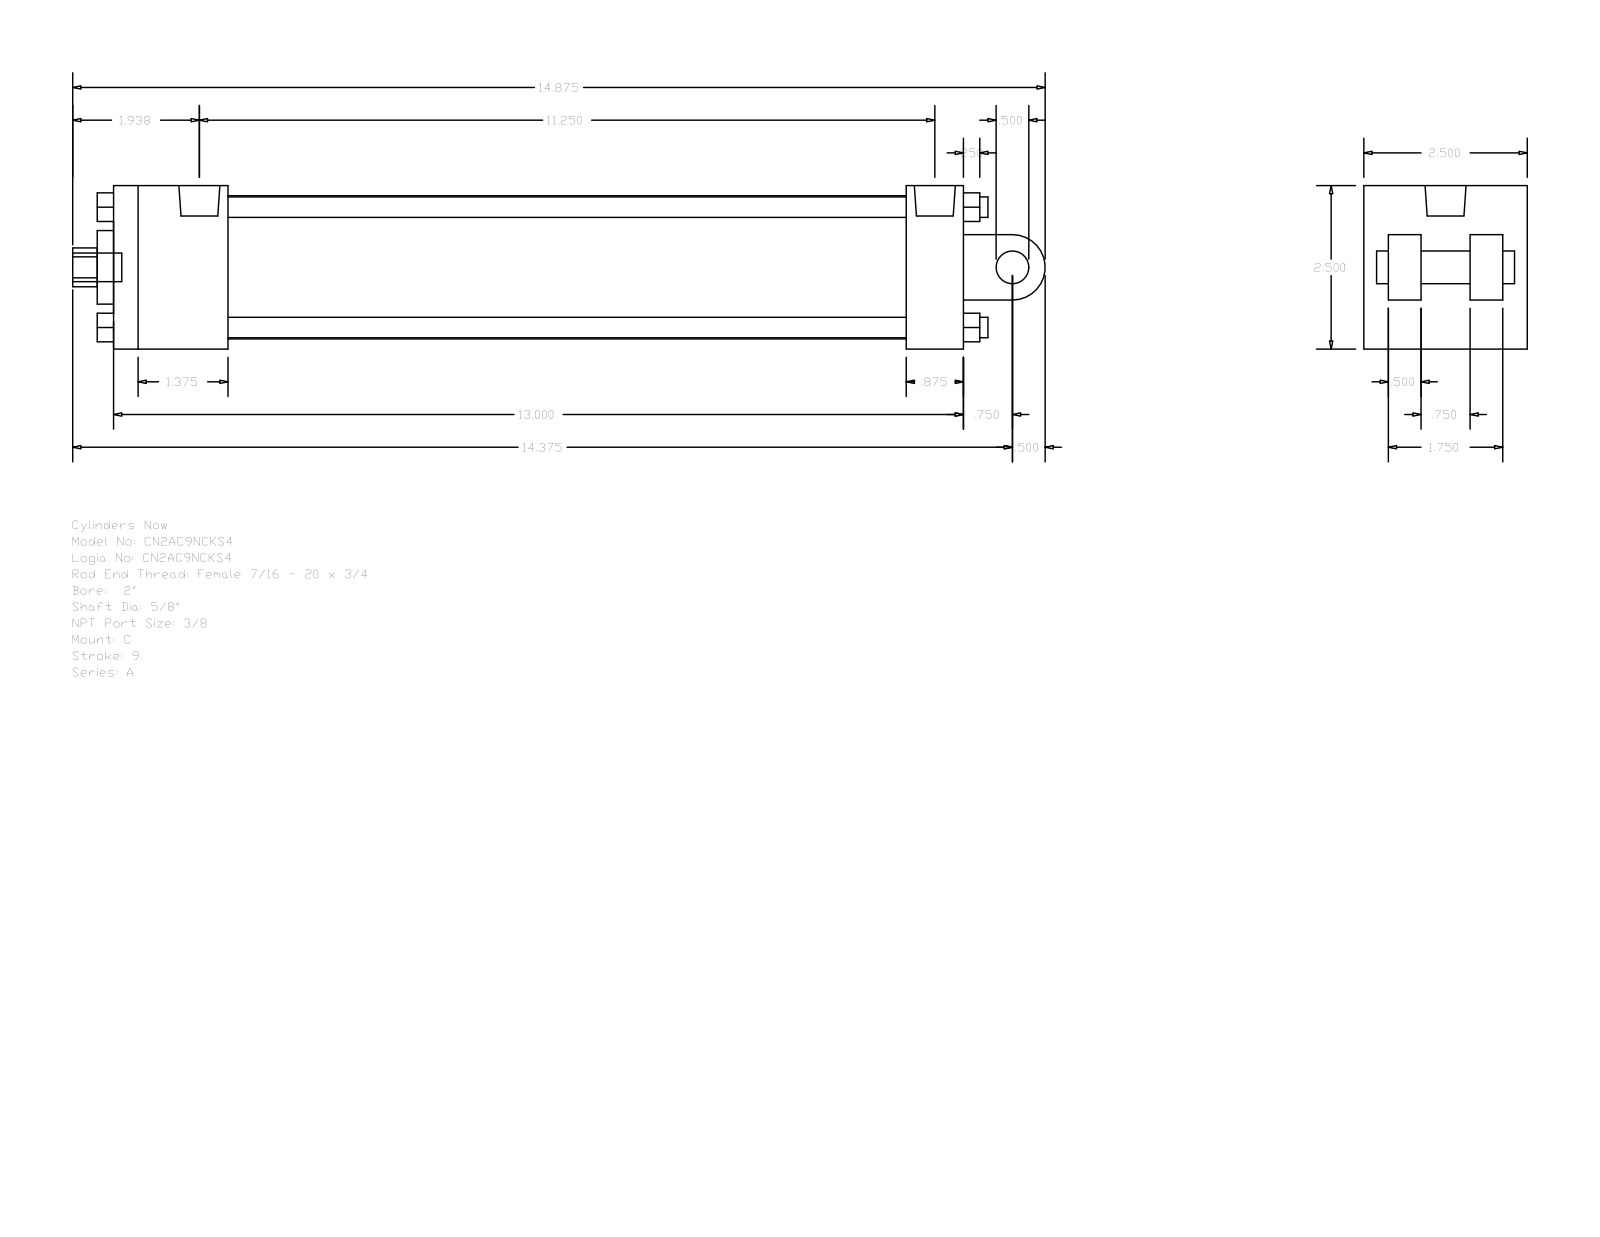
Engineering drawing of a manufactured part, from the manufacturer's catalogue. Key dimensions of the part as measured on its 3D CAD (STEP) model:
Part name (STEP PRODUCT): A_C__0200_0.625
STEP written by: GSSL Pune (CONFIG_CONTROL_DESIGN)
Units: millimetres
Bodies: 0 solids, 135 faces (102 planar, 33 cylindrical, 0 other)
Overall size (bounding box): 377.82 × 63.5 × 63.5
Round holes (diameter × count): ⌀5.56 ×2, ⌀15.88 ×1, ⌀15.93 ×1, ⌀28.57 ×1, ⌀55.63 ×1
Round bosses / shafts (diameter × count): ⌀7.94 ×4, ⌀5.56 ×2, ⌀15.93 ×1, ⌀12.7 ×1, ⌀11.11 ×1
Partial cylindrical surfaces — rounded edges, fillets, slot ends (radius × count): R7.54 ×1, R12.7 ×1
Main face-to-face distances: 63.5, 330.19, 22.22, 44.45, 285.74, 307.97, 263.52, 12.7, 41.28, 9.52
Hole centre spacings: 3.97
